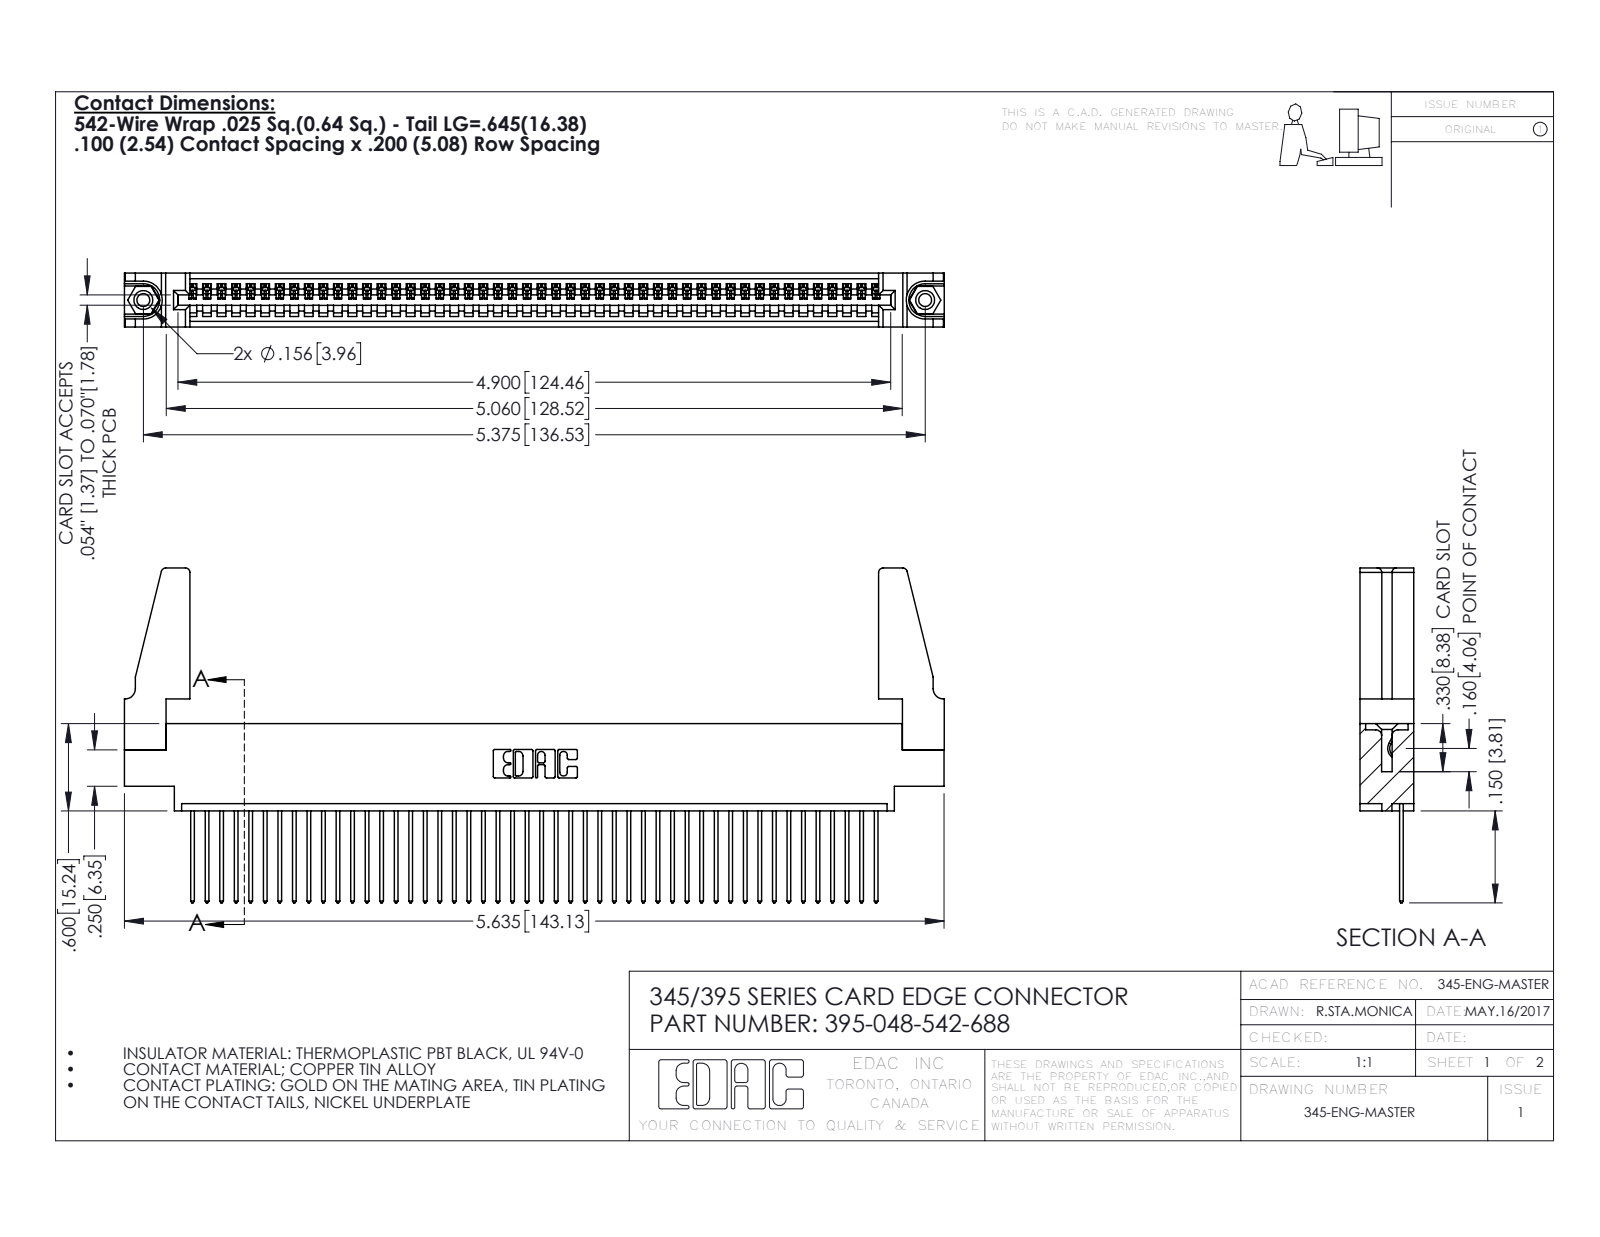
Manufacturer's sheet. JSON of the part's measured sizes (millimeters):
{"part_name": "345 Part_0.170 Offset - 0.156 Dia-TH; 345-250-001_345-250-001-102; 395-048-542-688; 345-220-078_345-220-088 (+1 more)", "step_written_by": "SolidWorks 2016 (CONFIG_CONTROL_DESIGN)", "units": "millimeters", "bodies": {"solids": 53, "faces": 3038, "planar": 2076, "cylindrical": 946, "other": 16}, "overall_size": [143.2, 58.5, 9.4], "volume_mm3": 16900, "surface_area_mm2": 22140, "round_holes": [[2.3, 2], [3.2, 2], [4, 2], [1.6, 1]], "round_bosses_or_shafts": [[3.9, 2]], "partial_cylinders_radius": [[0.2, 96], [0.3, 96], [0.3, 22], [0.8, 8], [0.2, 6], [0.8, 6], [0.7, 3], [0.8, 2]], "face_to_face_distances": [1.8, 7.6, 9.4, 2.5, 6.9, 0.6, 5.1, 5.7, 4.4, 3.8], "hole_center_spacings": [6.9, 130.5, 136.5]}
